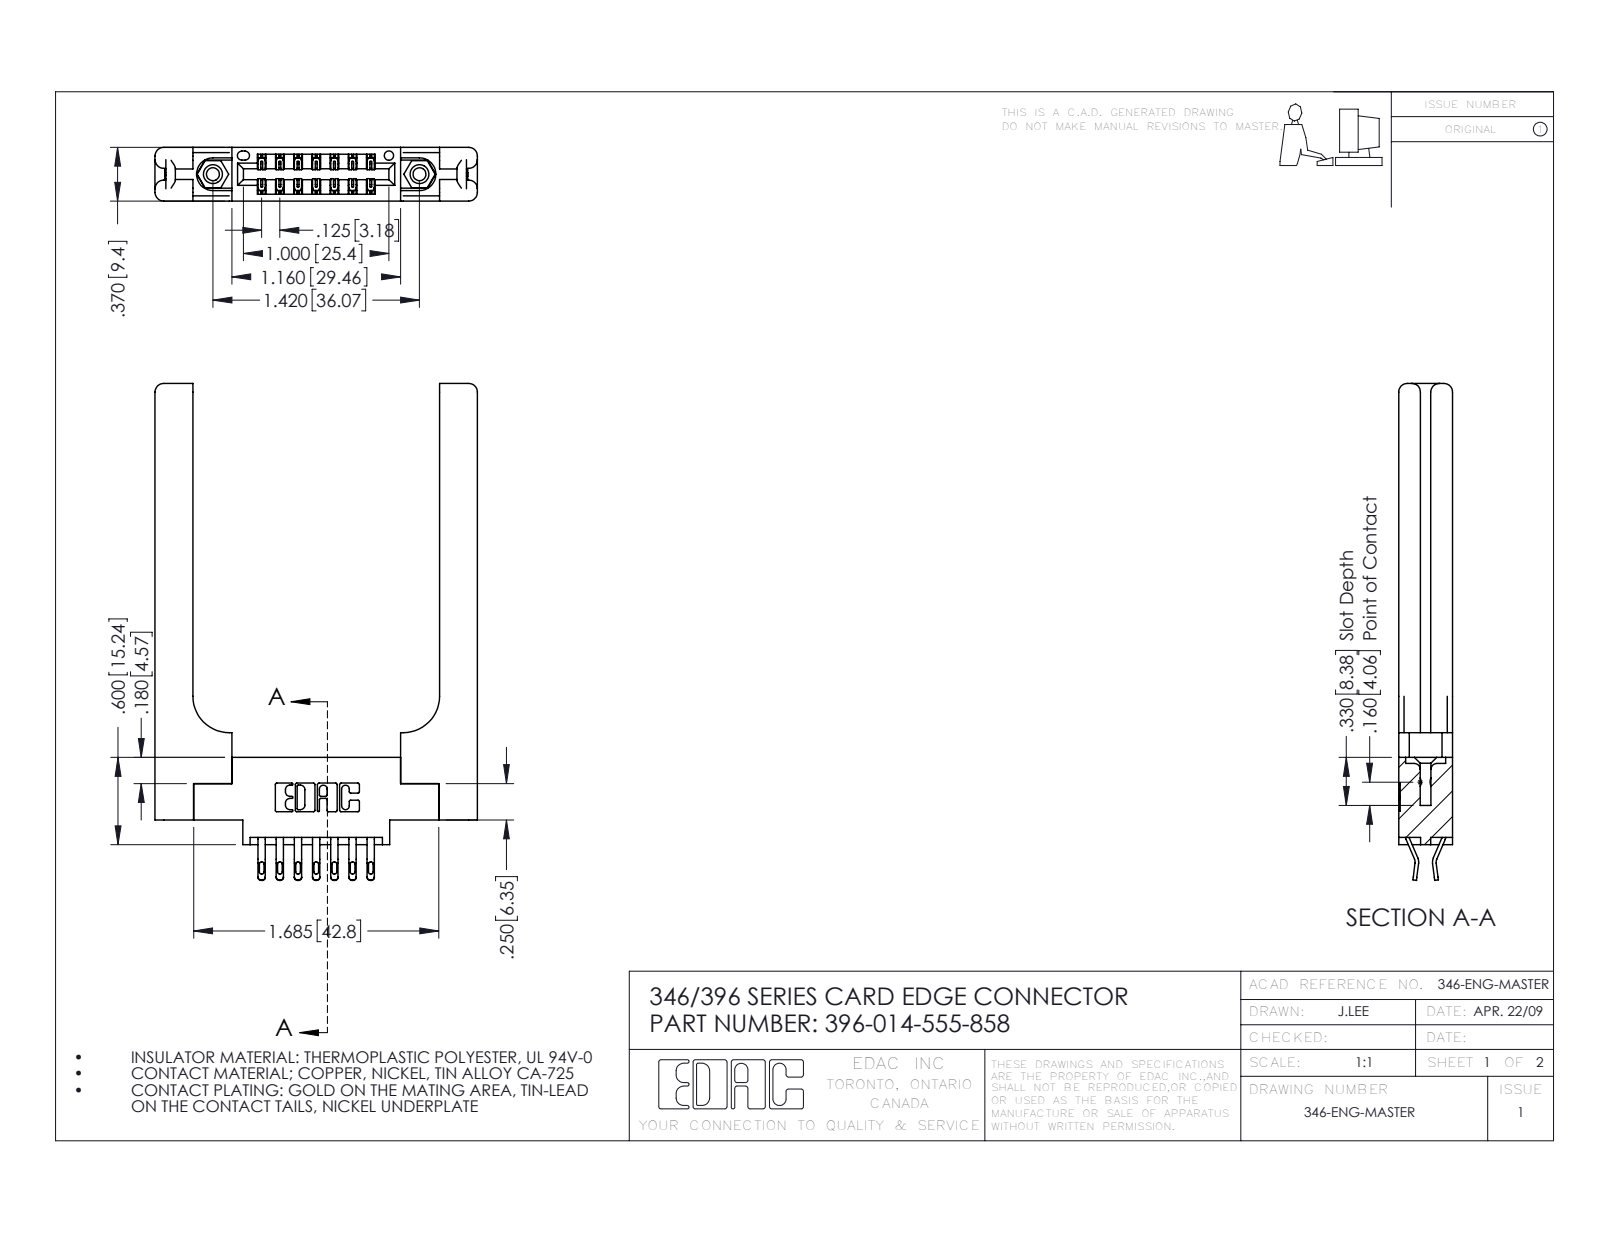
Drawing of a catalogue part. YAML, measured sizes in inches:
part_name: "346-220-058_345-220-058; 345-250-001_345-250-001-102; 396-014-555-858; 345-292-001_555 Tail (+1 more)"
step_written_by: "SolidWorks 2016 (CONFIG_CONTROL_DESIGN)"
units: inches
bodies: {solids: 19, faces: 1194, planar: 690, cylindrical: 444, other: 60}
overall_size: [3.415, 2.216, 0.37]
volume: 0.769
surface_area: 18.23
round_holes:
  - {diameter: 0.089, count: 2}
  - {diameter: 0.125, count: 2}
  - {diameter: 0.156, count: 2}
  - {diameter: 0.064, count: 1}
round_bosses_or_shafts:
  - {diameter: 0.155, count: 2}
partial_cylinders:
  - {radius: 0.016, count: 28}
  - {radius: 0.02, count: 28}
  - {radius: 0.01, count: 22}
  - {radius: 0.006, count: 21}
  - {radius: 0.06, count: 16}
  - {radius: 0.007, count: 6}
  - {radius: 0.031, count: 6}
  - {radius: 0.026, count: 3}
face_to_face_distances: [0.37, 0.15, 0.22, 0.072, 0.148, 0.25, 1.696, 0.102, 0.048, 0.322]
hole_center_spacings: [0.246, 1.217, 1.42]
